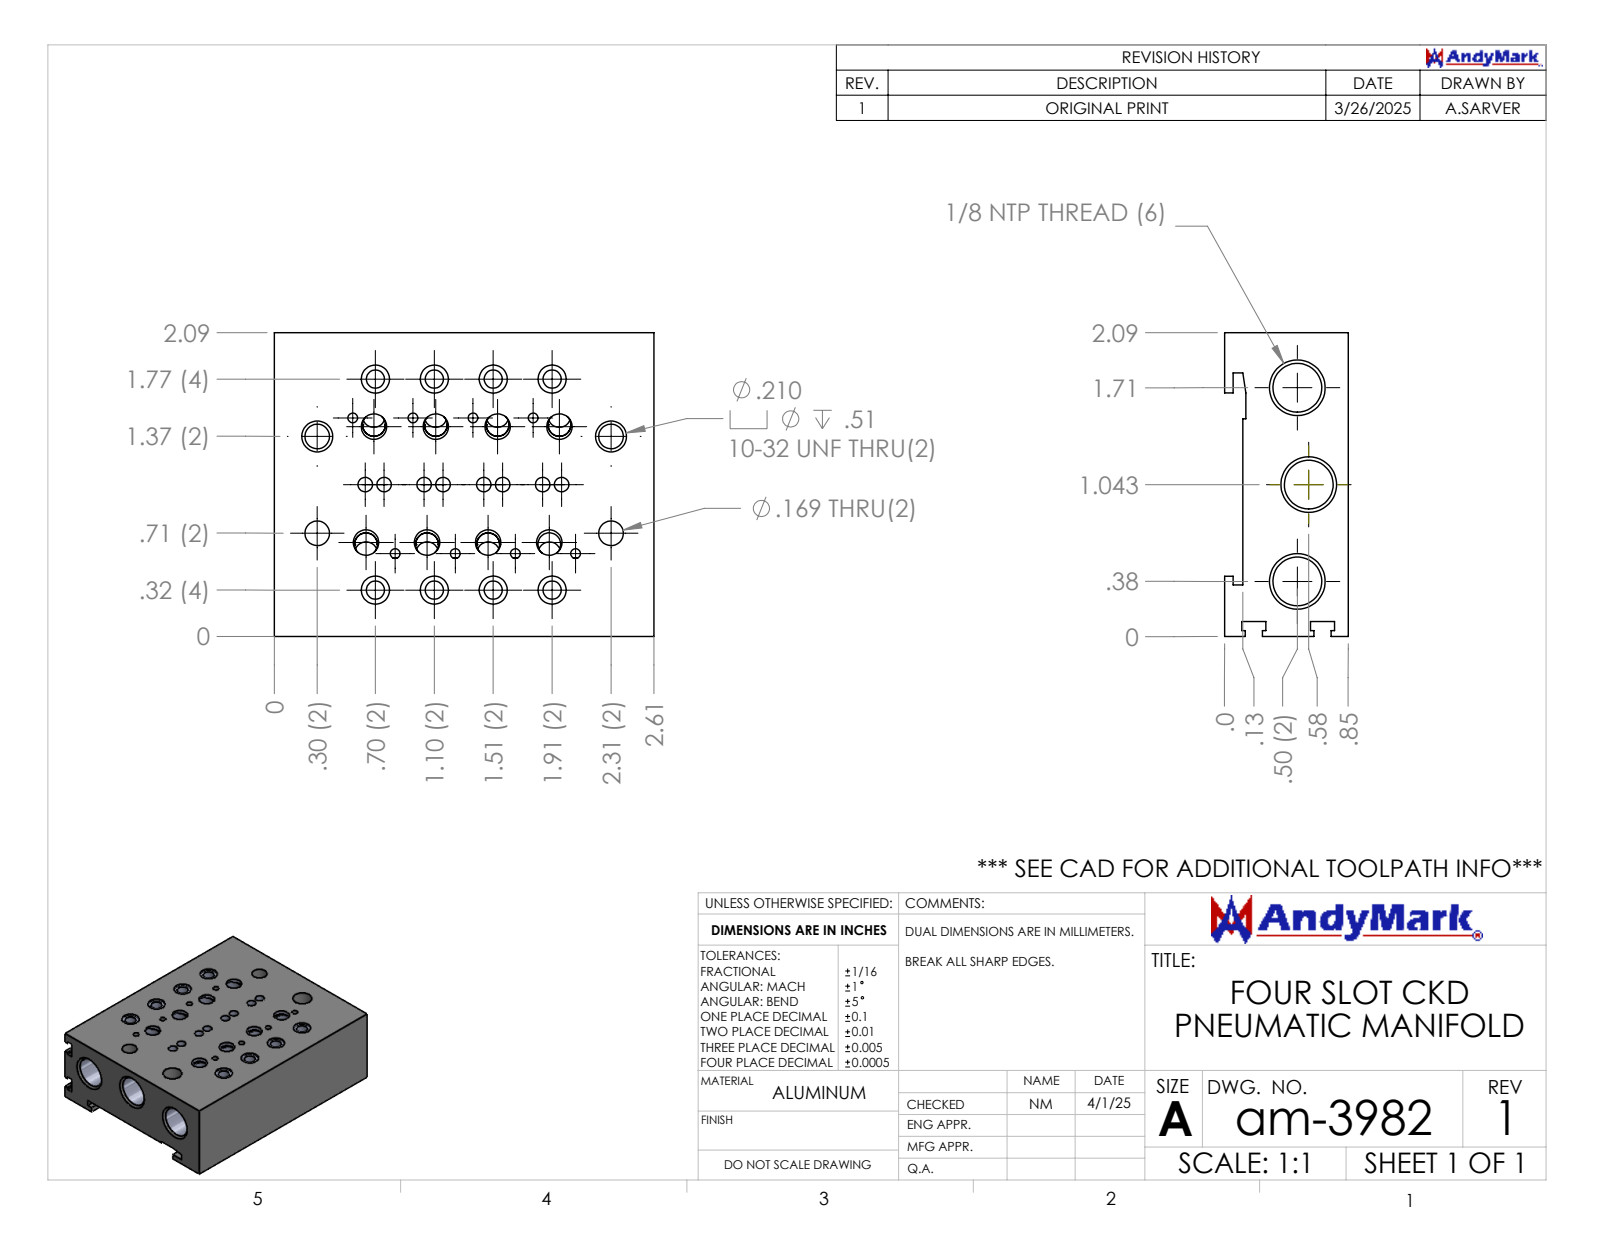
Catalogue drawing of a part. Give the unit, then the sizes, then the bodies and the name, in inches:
Units: inches
Overall size (bounding box): 2.61 × 2.087 × 0.85
Round holes (diameter × count): ⌀0.067 ×8, ⌀0.1 ×8, ⌀0.175 ×8, ⌀0.193 ×8, ⌀0.157 ×7, ⌀0.125 ×6, ⌀0.169 ×4, ⌀0.336 ×3, ⌀0.125 ×2, ⌀0.213 ×2, ⌀0.156 ×1
Partial cylindrical surfaces — rounded edges, fillets, slot ends (radius × count): R0.078 ×7
Main face-to-face distances: 0.724, 0.126, 0.85, 2.087, 2.61, 0.102, 1.984, 0.059, 0.472, 0.067
Hole centre spacings: 0.728, 0.405, 0.405, 0.413, 0.864, 1.506, 0.8, 0.815
Volume: 3.193 in³ · Surface area: 33.98 in²
Bodies: 1 solid, 240 faces (73 planar, 135 cylindrical, 32 other)
Part name (STEP PRODUCT): am-3982 Four Slot CKD Pneumatic Manifold
STEP written by: SolidWorks 2024 (CONFIG_CONTROL_DESIGN)
